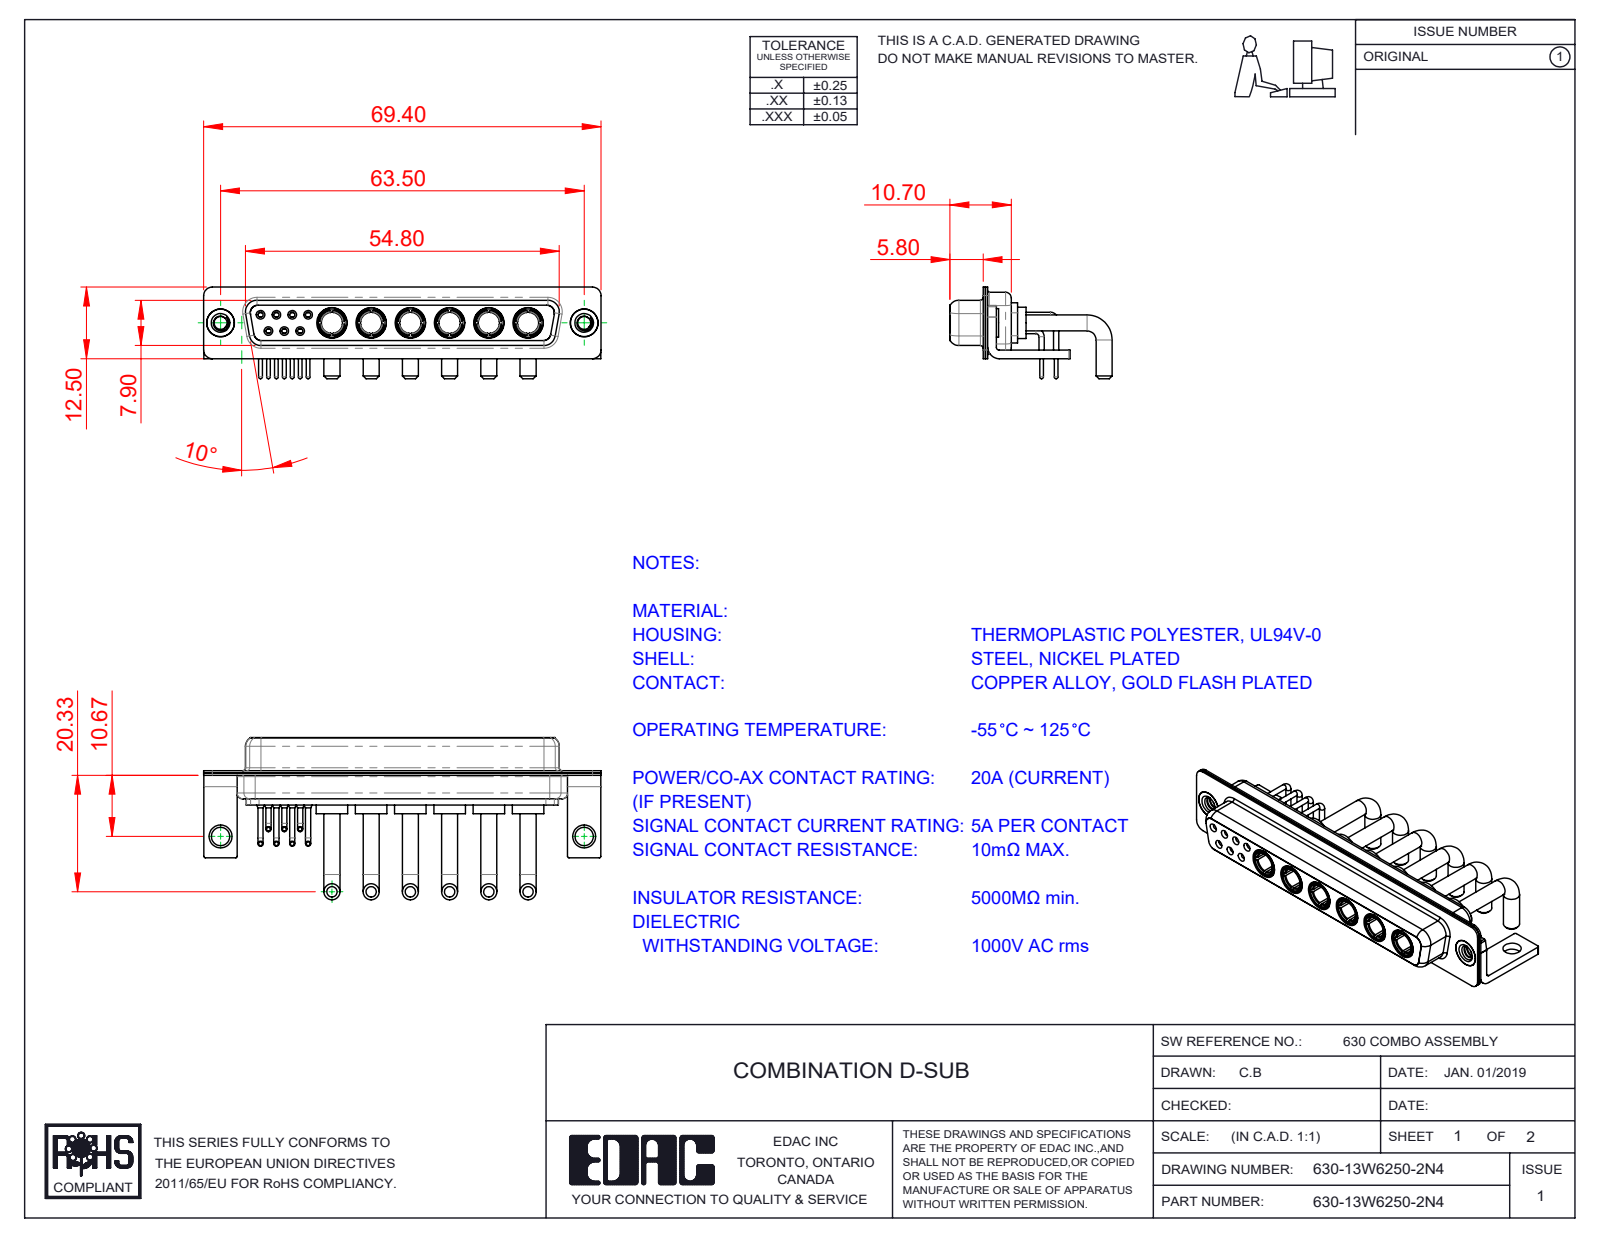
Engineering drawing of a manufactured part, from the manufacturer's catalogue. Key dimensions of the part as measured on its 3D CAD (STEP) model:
Part name (STEP PRODUCT): 630-13W6250-2N4; 630Combo Shell Front_37 Contacts; 630Combo Threaded Rivet_3; 630Combo Contact Row 1 (+5 more)
STEP written by: SolidWorks 2020 (CONFIG_CONTROL_DESIGN)
Units: millimetres
Bodies: 26 solids, 1158 faces (366 planar, 466 cylindrical, 326 other)
Overall size (bounding box): 69.4 × 28.33 × 16
Volume: 6 206 mm³ · Surface area: 13 189 mm²
Round holes (diameter × count): ⌀4.85 ×8, ⌀0.9 ×7, ⌀1.1 ×7, ⌀1.5 ×7, ⌀2 ×7, ⌀3.7 ×6, ⌀5.3 ×6, ⌀1.7 ×4, ⌀1.6 ×3, ⌀2.26 ×2, ⌀3.2 ×2, ⌀4 ×2
Round bosses / shafts (diameter × count): ⌀2.8 ×12, ⌀0.9 ×7, ⌀0.65 ×7, ⌀5.5 ×6, ⌀5.2 ×6, ⌀4.96 ×6, ⌀4.75 ×6, ⌀3.75 ×6
Partial cylindrical surfaces — rounded edges, fillets, slot ends (radius × count): R0.25 ×16, R1.5 ×16, R2 ×13, R1.35 ×8, R1.6 ×8, R2.1 ×6, R0.5 ×5, R0.6 ×4
Main face-to-face distances: 0.4, 0.45, 1.4, 8.45, 1.8, 8.9, 7.05, 6.2, 7.5, 0.8
Hole centre spacings: 3.16, 2.77, 6.85, 13.7, 5.54, 20.55, 5.03, 5.04
